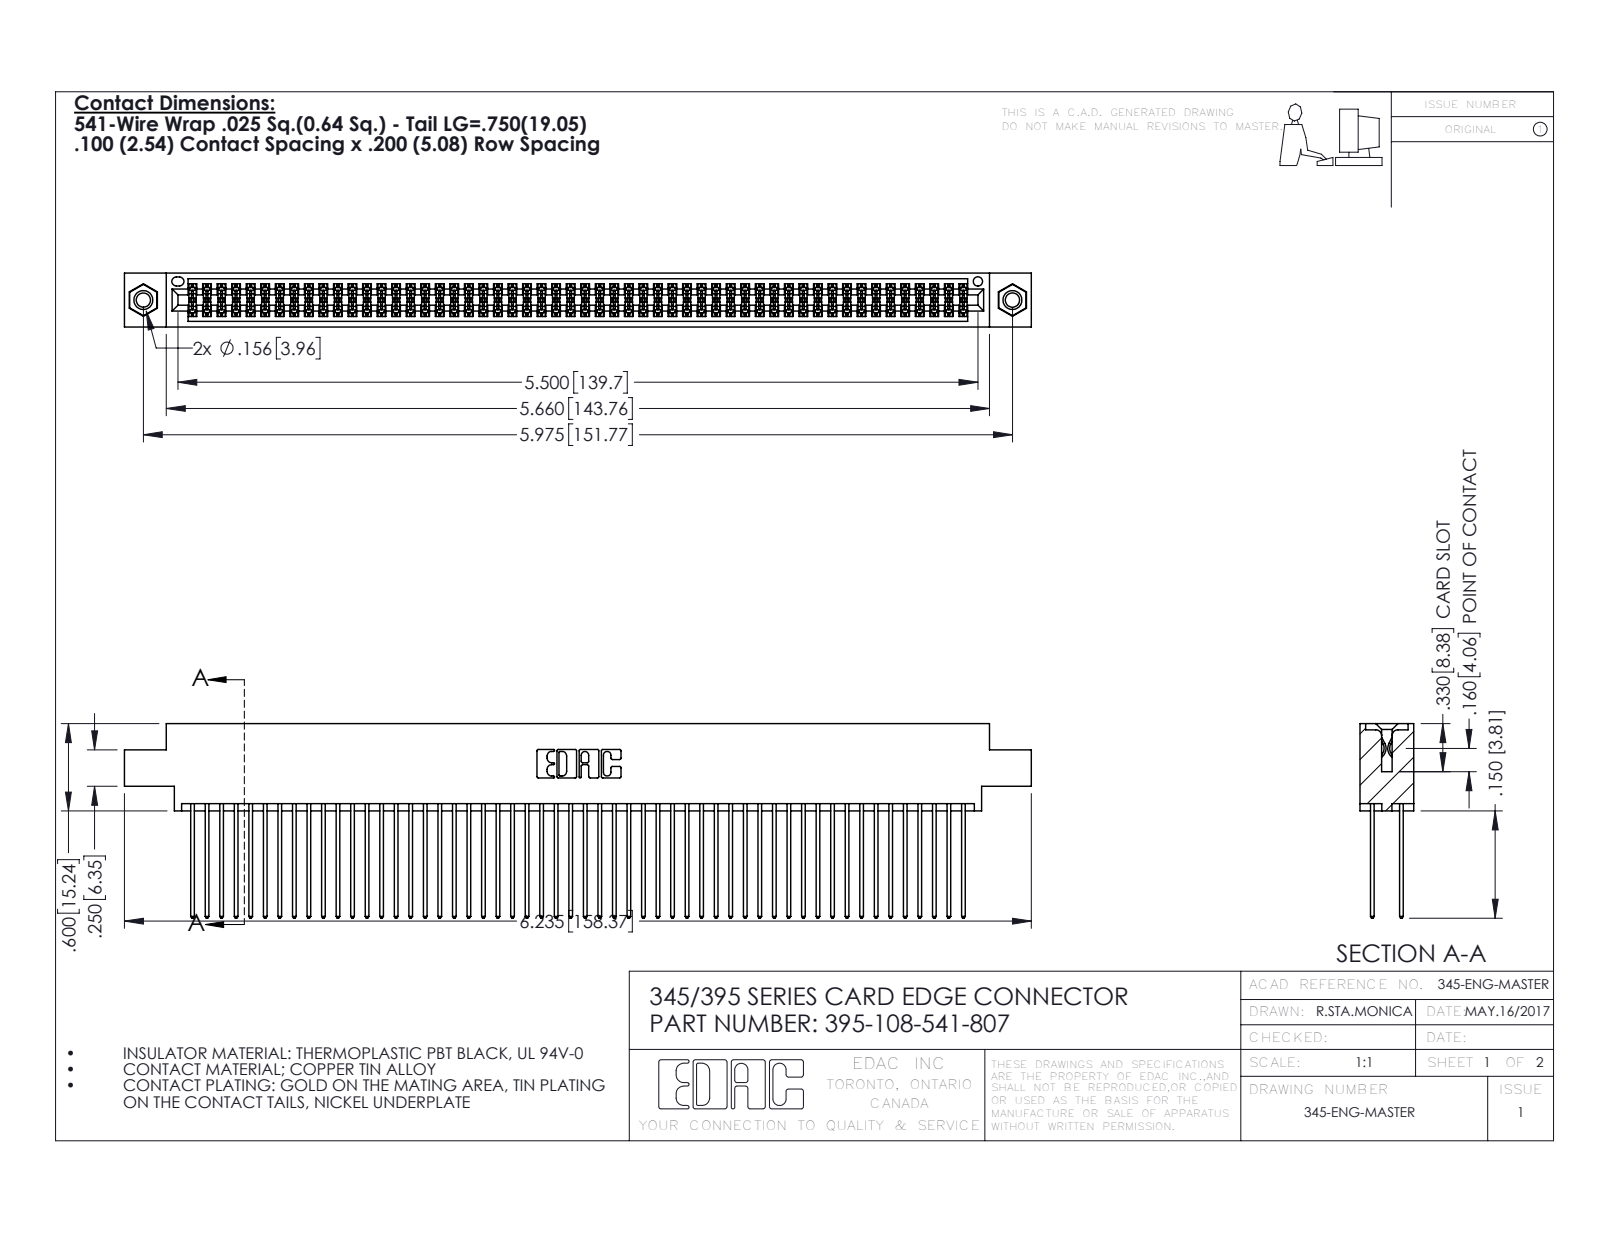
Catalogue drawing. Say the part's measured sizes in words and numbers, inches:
The part is named "345-292-001_345-293-141; 345-250-001_345-250-005-103; 345 Part_0.170 Offset - 0.156 Dia-TI; 395-108-541-807". Its 3-D file was written by "SolidWorks 2016 (CONFIG_CONTROL_DESIGN)". It is 111 solids with 5590 faces: 3680 planar, 1894 cylindrical and 16 other. Overall it measures 6.235 by 1.337 by 0.37 inches. Its volume is 0.976 cubic inches and its surface area 41.77 square inches. Round holes: 2 of diameter 0.098, 2 of diameter 0.125, 2 of diameter 0.156, 1 of diameter 0.064. Round bosses or shafts: 2 of diameter 0.155. Partial cylindrical surfaces (rounded edges, fillets, slot ends): 162 of radius 0.006, 108 of radius 0.01, 22 of radius 0.01, 6 of radius 0.007, 6 of radius 0.031, 3 of radius 0.026, 2 of radius 0.014, 2 of radius 0.019. The main face-to-face distances are 0.072, 0.298, 0.2, 0.098, 0.272, 0.025, 0.225, 0.37, 0.175, 0.149. The hole center spacings are 0.27, 5.739, 5.975.
